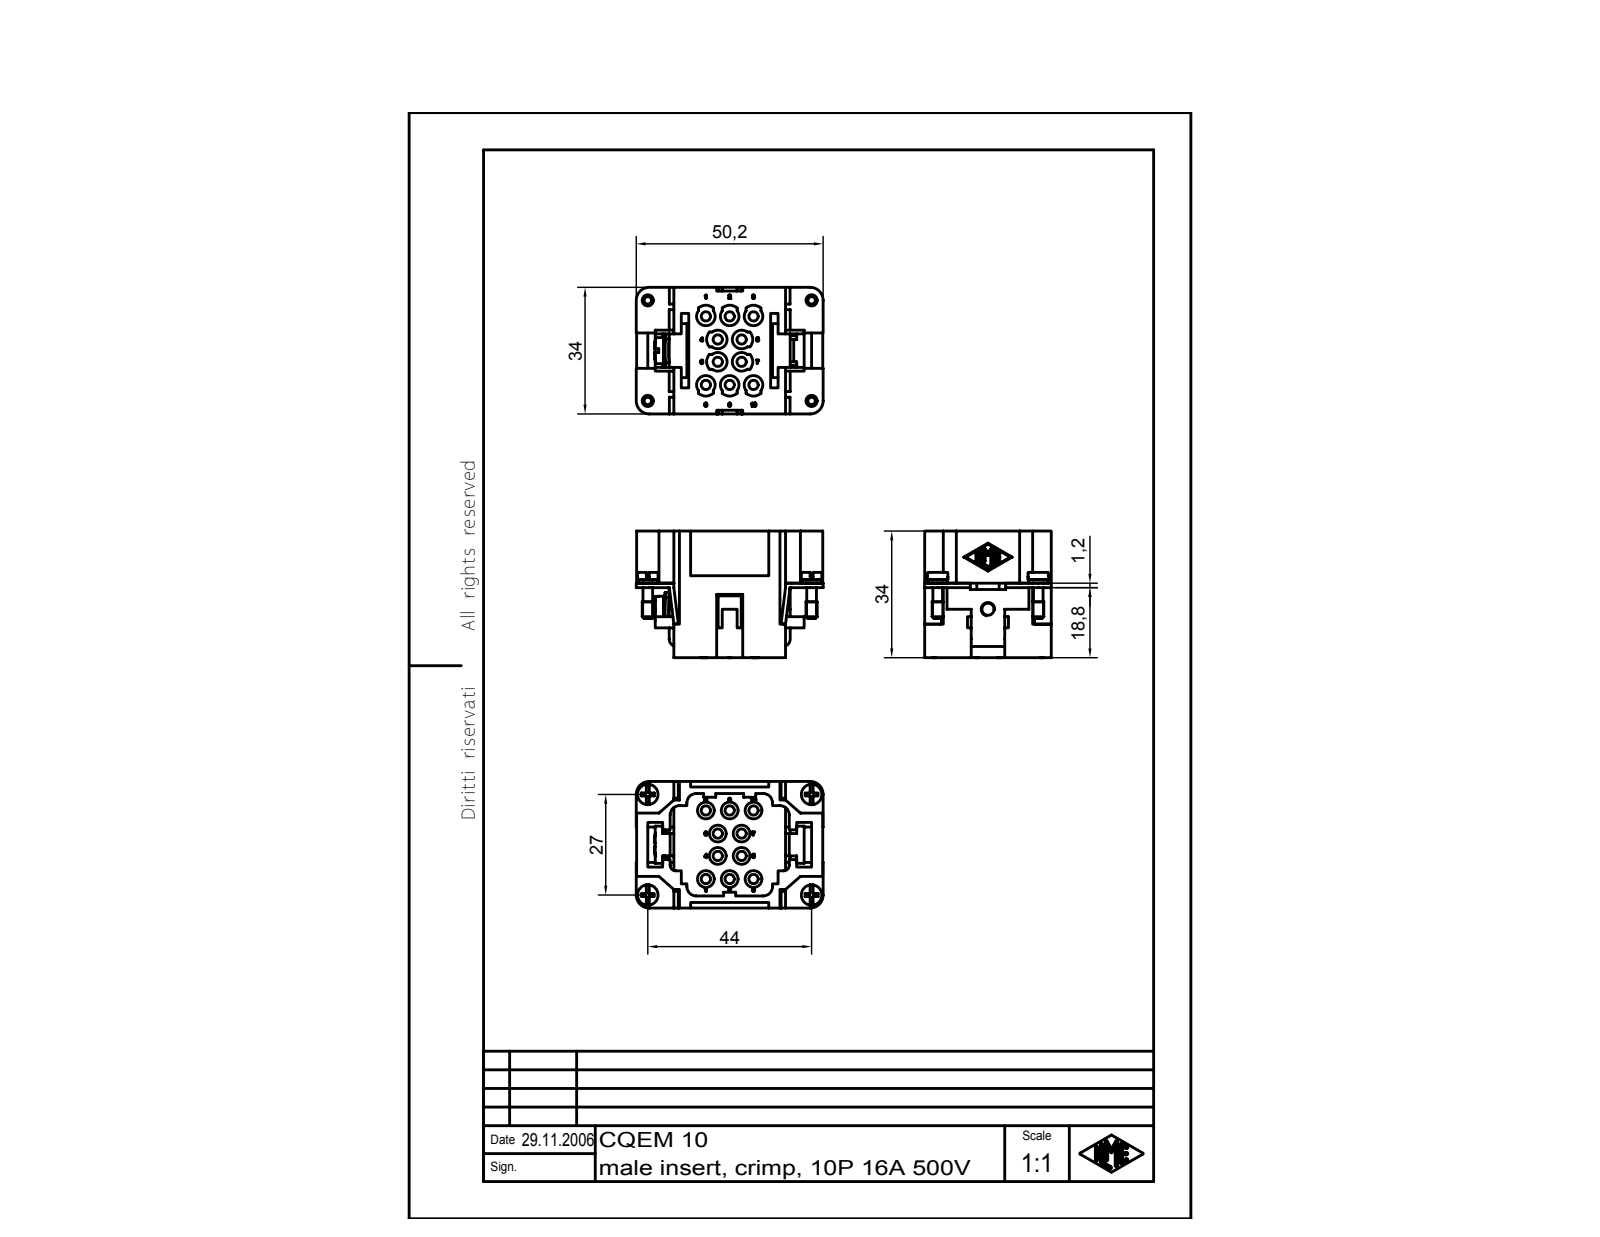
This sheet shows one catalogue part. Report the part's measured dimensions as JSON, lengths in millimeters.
{"part_name": "CQEM 10", "step_written_by": "Autodesk Inventor 7 (AUTOMOTIVE_DESIGN)", "units": "millimeters", "bodies": {"solids": 2, "faces": 911, "planar": 403, "cylindrical": 119, "other": 389}, "overall_size": [50.2, 34.01, 34], "volume_mm3": 23363, "surface_area_mm2": 17462, "round_holes": [[2.5, 10], [3.24, 1]], "round_bosses_or_shafts": [[4.5, 10], [5.5, 2], [5.3, 2], [3, 2], [2.6, 2], [7, 1]], "partial_cylinders_radius": [[0.25, 14], [2.5, 11], [3, 5], [2, 4], [1.5, 2], [3.5, 2], [5.5, 1]], "face_to_face_distances": [34, 20, 1.5, 7, 2, 10, 3, 3.25, 8.5, 14], "hole_center_spacings": [6.98, 12.61, 6.4, 11.43, 15.52, 19.48, 18.4, 6]}
